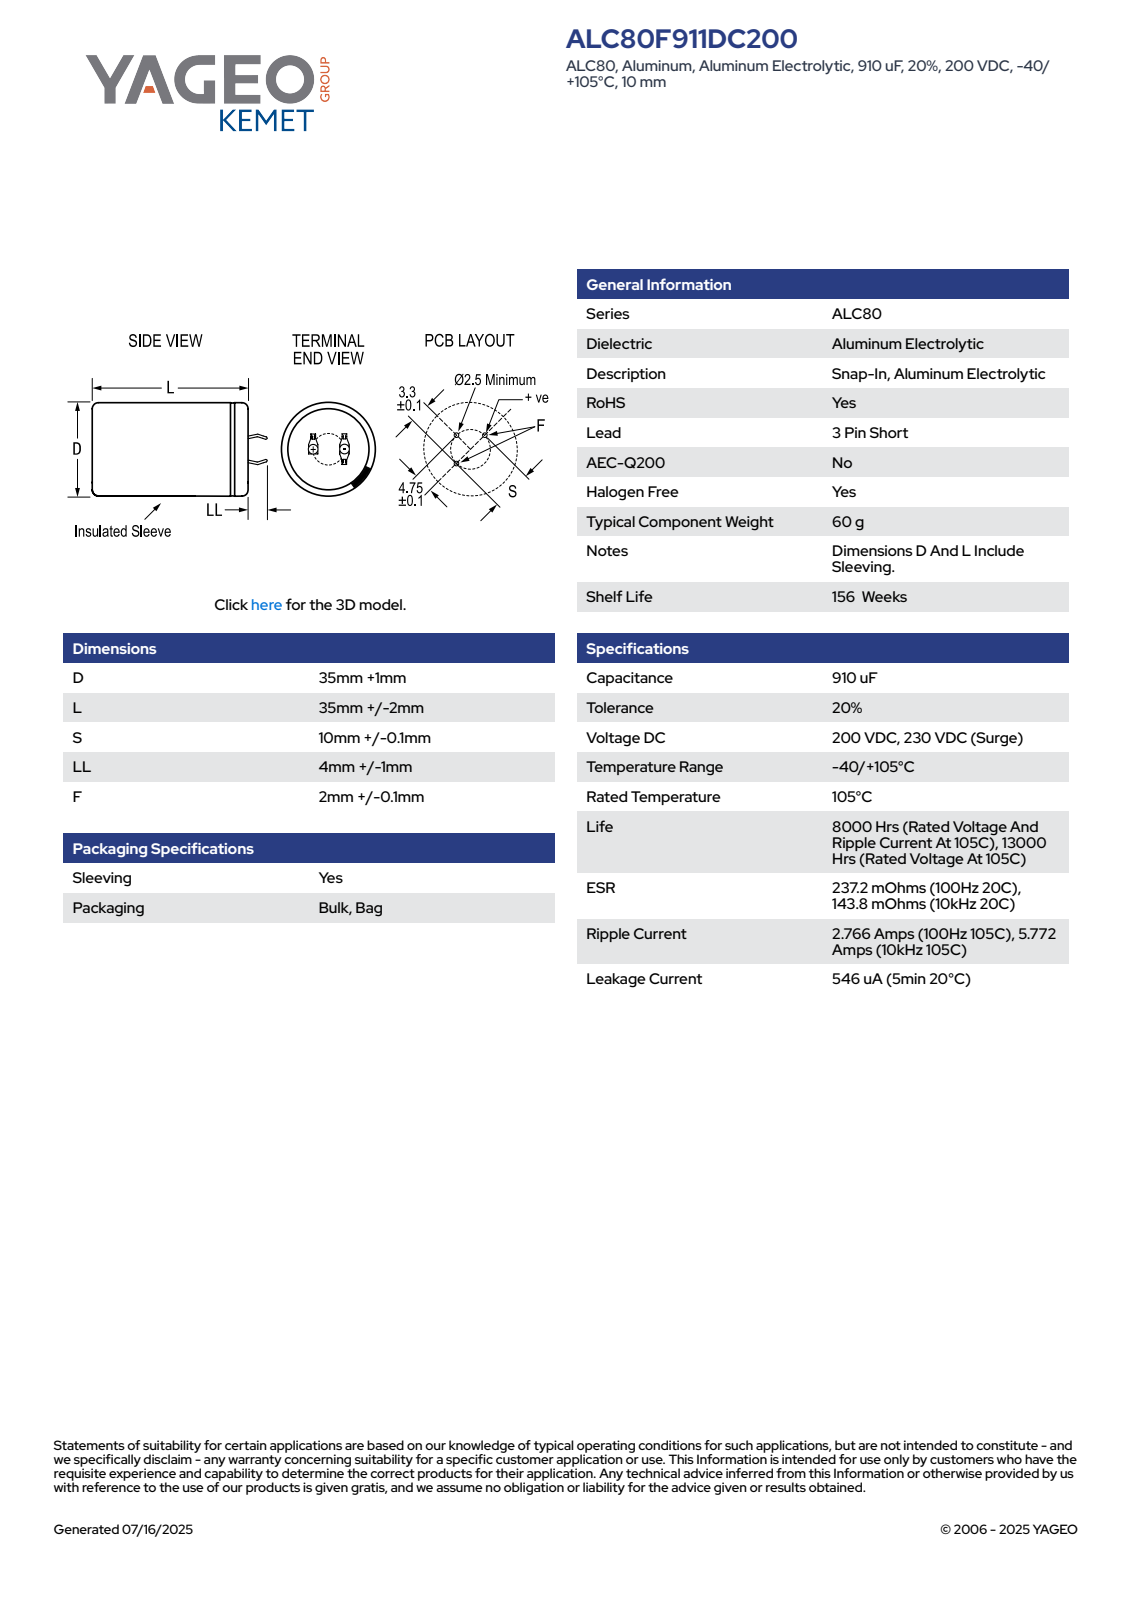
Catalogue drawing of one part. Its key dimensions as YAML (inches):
part_name: "CARS_K3P_35X35_D36L37S10LL5F2.1"
step_written_by: "SolidWorks 2014 (AUTOMOTIVE_DESIGN)"
units: inches
bodies: {solids: 1, faces: 115, planar: 61, cylindrical: 15, other: 39}
overall_size: [1.653, 1.417, 1.417]
volume: 2.266
surface_area: 9.636
round_holes:
  - {diameter: 1.254, count: 1}
round_bosses_or_shafts:
  - {diameter: 1.417, count: 1}
partial_cylinders:
  - {radius: 0.708, count: 1}
face_to_face_distances: [1.456, 1.476, 0.02, 0.024, 0.324, 0.03, 0.053, 0.023, 0.023, 0.294]
